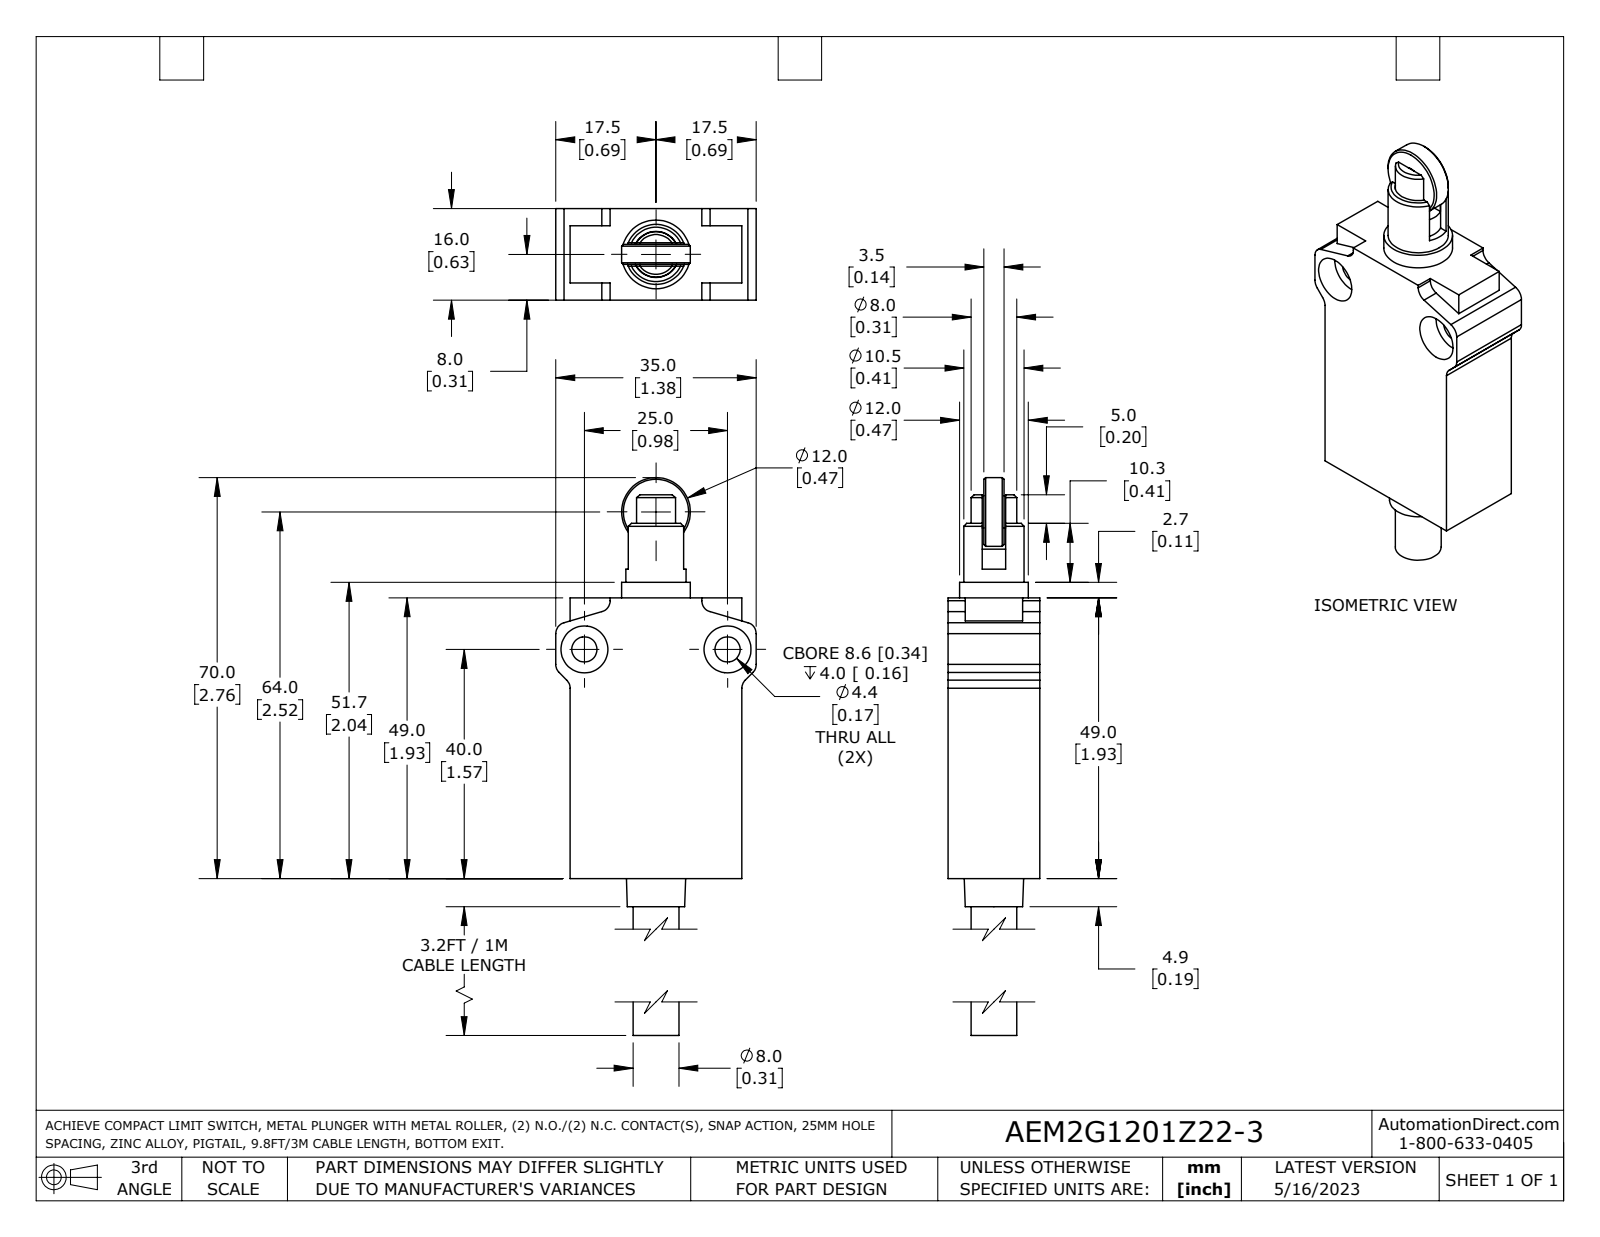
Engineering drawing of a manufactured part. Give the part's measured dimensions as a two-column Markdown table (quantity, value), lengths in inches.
| quantity | value |
| --- | --- |
| part name | AEM2G1201Z22-3 |
| STEP written by | SolidWorks 2021 (AUTOMOTIVE_DESIGN) |
| units | inches |
| bodies | 1 solid, 99 faces (59 planar, 29 cylindrical, 11 other) |
| overall size | 3.343 × 1.378 × 0.63 |
| volume | 1.527 in³ |
| surface area | 12.66 in² |
| round holes (diameter × count) | 0.173 × 2, 0.323 × 2, 0.317 × 1 |
| round bosses / shafts (diameter × count) | 0.472 × 2, 0.413 × 1, 0.315 × 1, 0.313 × 1, 0.22 × 1 |
| partial cylindrical surfaces (radius × count) | 0.079 × 8, 0.256 × 1 |
| main face-to-face distances | 0.63, 1.181, 1.929, 0.15, 0.098, 1.28, 0.246, 0.384, 0.472, 0.157 |
| hole center spacings | 0.984 |
